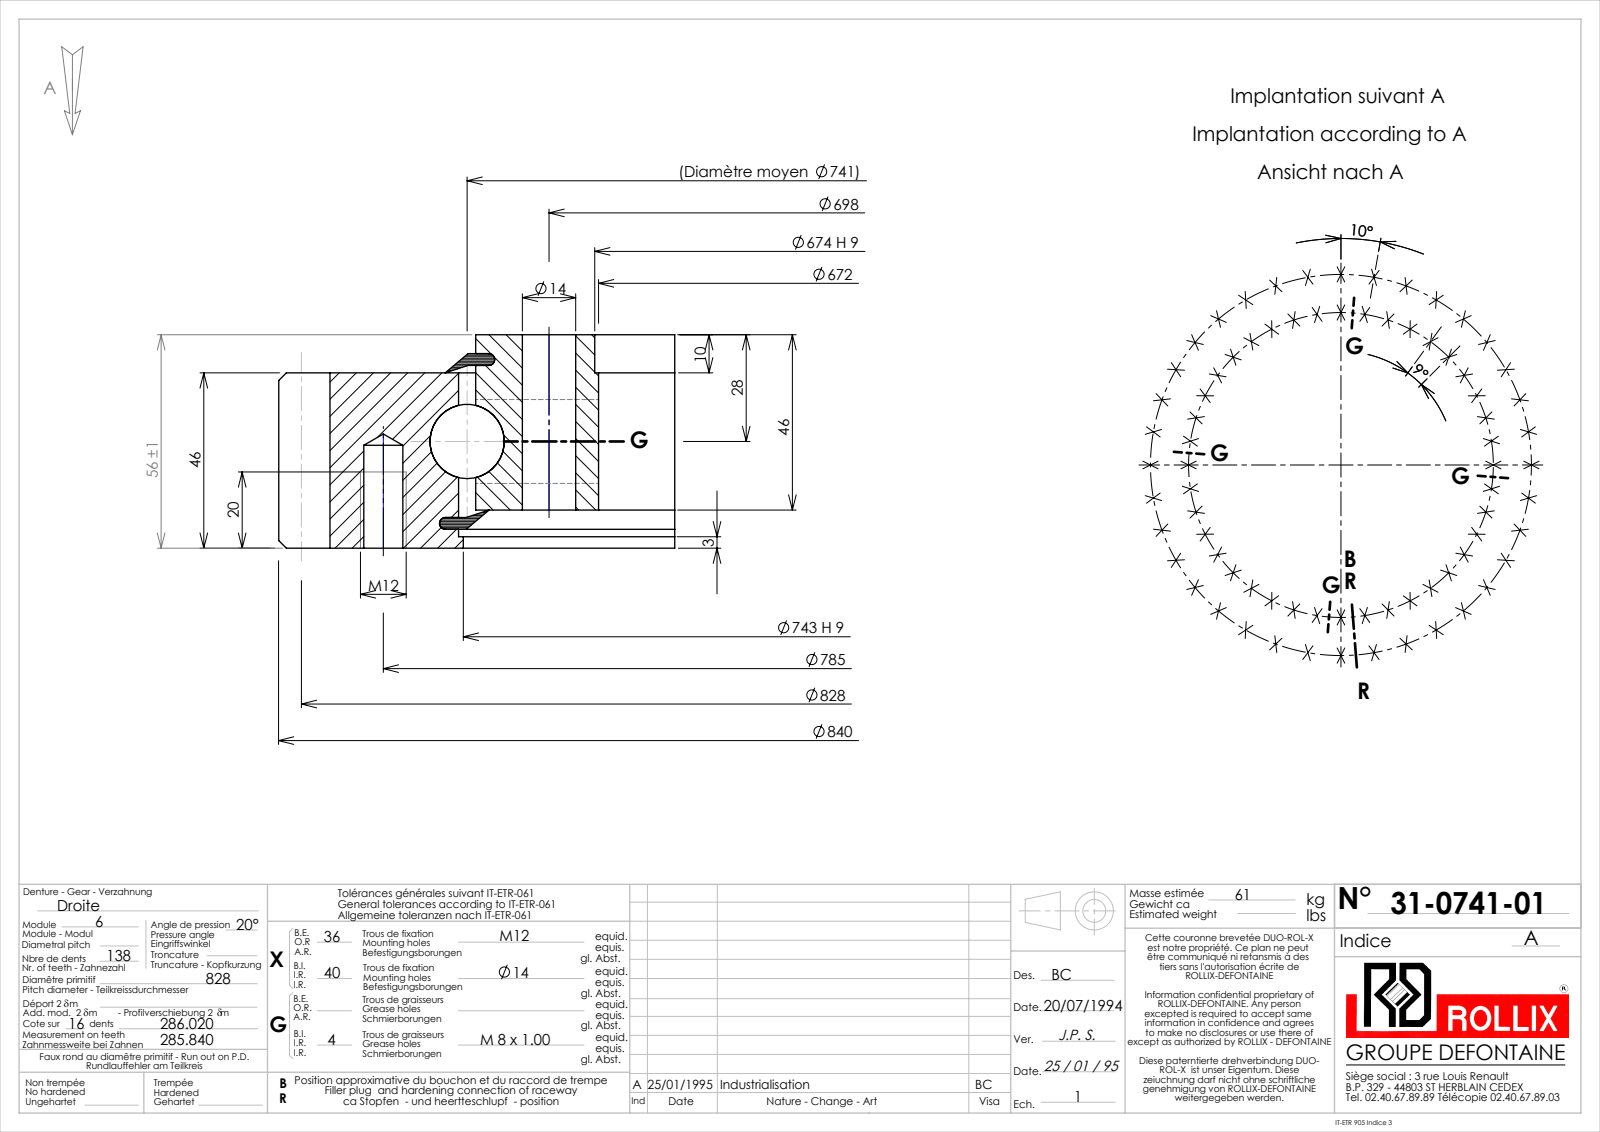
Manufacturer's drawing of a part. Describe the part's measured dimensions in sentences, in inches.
The part is named "31-0741-01". Its 3-D file was written by "SolidWorks 2016 (CONFIG_CONTROL_DESIGN)". It is 9 solids with 1209 faces: 330 planar, 463 cylindrical and 416 other. Overall it measures 33.071 by 33.067 by 2.205 inches. Its volume is 435.3 cubic inches and its surface area 1 888 square inches. Round holes: 40 of diameter 0.551, 36 of diameter 0.404, 4 of diameter 0.276, 1 of diameter 26.457, 1 of diameter 26.535, 1 of diameter 29.252, 1 of diameter 29.35. Round bosses or shafts: 4 of diameter 0.315, 1 of diameter 28.996. Partial cylindrical surfaces (rounded edges, fillets, slot ends): 1 of radius 16.004, 1 of radius 16.535. The main face-to-face distances are 1.811, 0.394, 1.417, 2.205, 0.199, 0.077, 1.693, 0.195, 2.01, 1.616. The hole center spacings are 5.367, 28.01, 7.999, 25.316, 26.765, 29.852, 30.436, 10.57.
